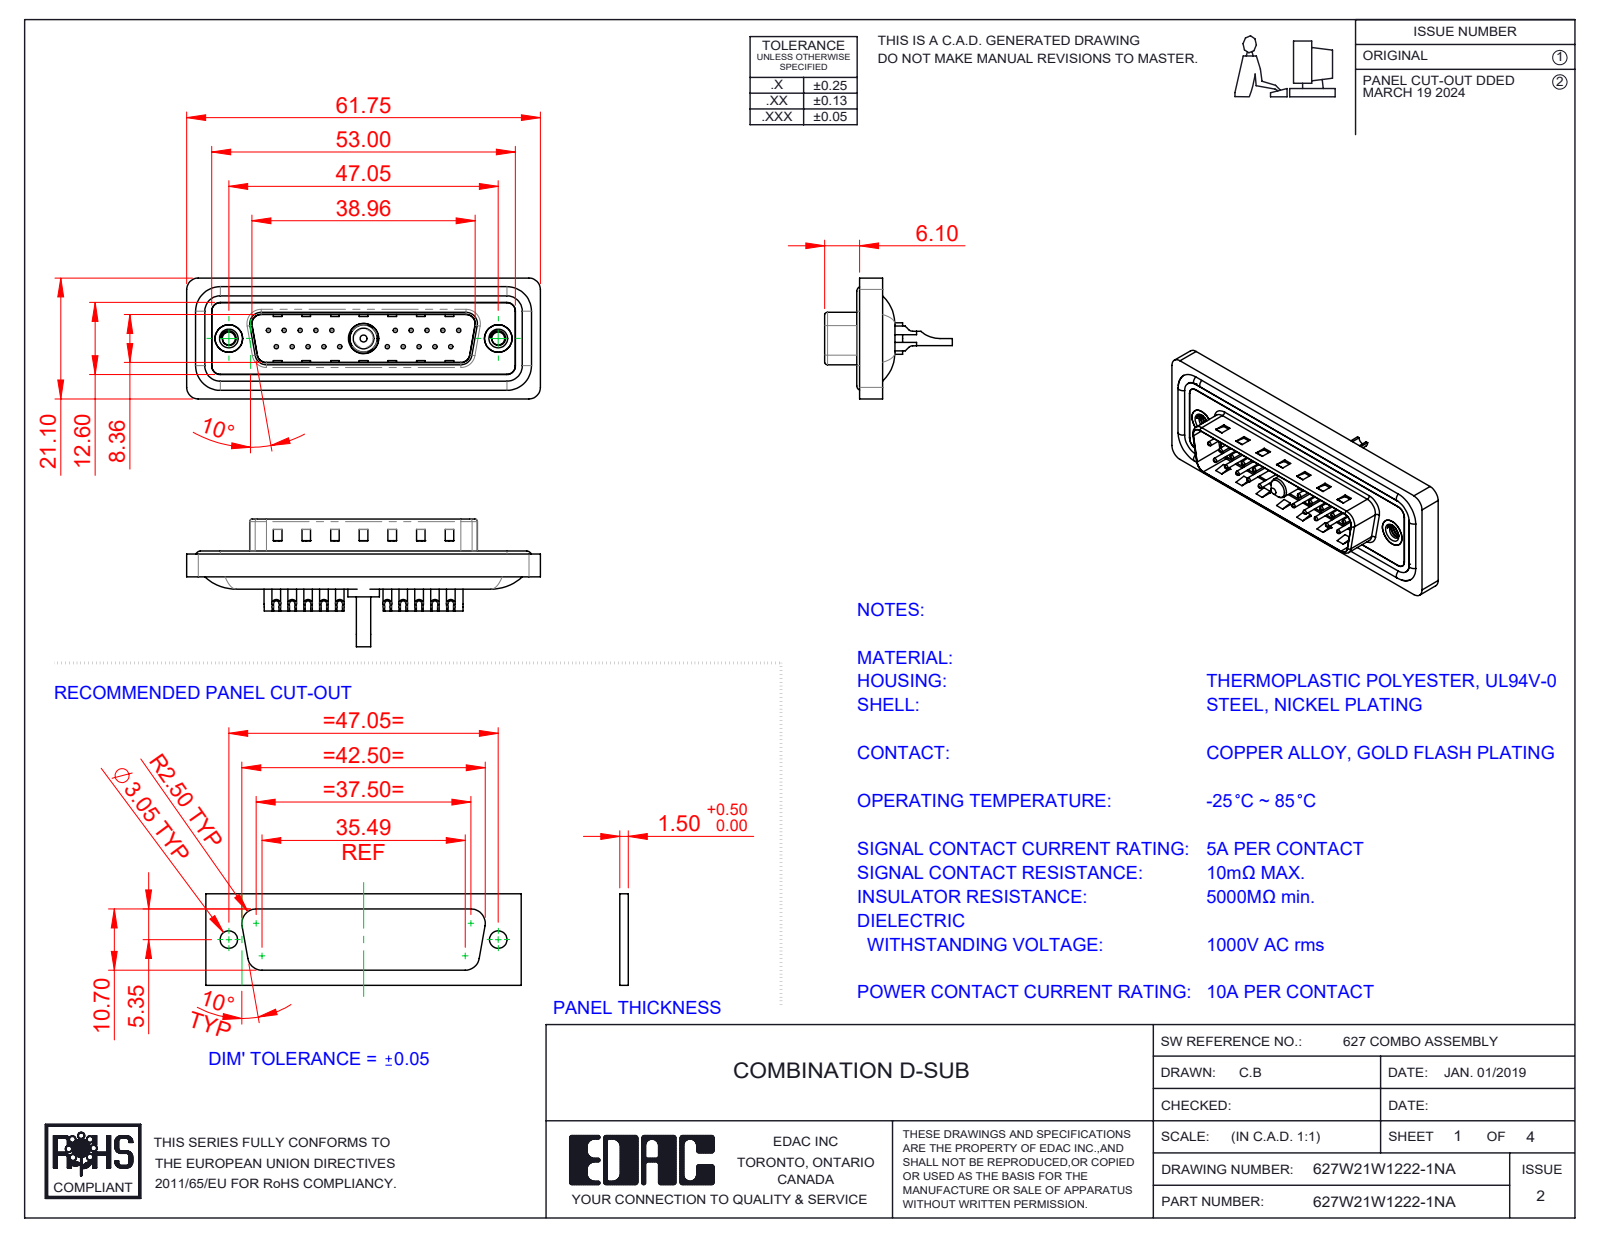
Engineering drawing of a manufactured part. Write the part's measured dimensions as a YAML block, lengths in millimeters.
part_name: "627Combo Waterproof Housing_25 Contacts; 627W21W1222-1NA; 627Combo Shell Rear_25 Contacts; 627Combo Contact Row 2_22 (+5 more)"
step_written_by: "SolidWorks 2023 (CONFIG_CONTROL_DESIGN)"
units: millimeters
bodies: {solids: 29, faces: 1266, planar: 401, cylindrical: 532, other: 333}
overall_size: [61.75, 22.3, 21.1]
volume: 7227
surface_area: 12158
round_holes:
  - {diameter: 0.75, count: 20}
  - {diameter: 1, count: 20}
  - {diameter: 1.6, count: 20}
  - {diameter: 2, count: 20}
  - {diameter: 2.26, count: 2}
  - {diameter: 4, count: 2}
  - {diameter: 4.8, count: 2}
  - {diameter: 5, count: 2}
  - {diameter: 1.7, count: 1}
  - {diameter: 4.85, count: 1}
  - {diameter: 5.3, count: 1}
round_bosses_or_shafts:
  - {diameter: 1.5, count: 20}
  - {diameter: 1.6, count: 4}
  - {diameter: 4.9, count: 2}
  - {diameter: 5.5, count: 1}
  - {diameter: 5.2, count: 1}
  - {diameter: 4.75, count: 1}
  - {diameter: 3.75, count: 1}
  - {diameter: 3.6, count: 1}
partial_cylinders:
  - {radius: 1.5, count: 22}
  - {radius: 2, count: 18}
  - {radius: 0.5, count: 8}
  - {radius: 1.6, count: 8}
  - {radius: 1, count: 6}
  - {radius: 0.25, count: 4}
  - {radius: 0.6, count: 4}
  - {radius: 0.65, count: 4}
face_to_face_distances: [0.4, 1.5, 1.1, 1.6, 0.5, 3.1, 2.9, 4.1, 0.82, 9.58]
hole_center_spacings: [3.16, 2.77, 5.54, 8.31, 5.04, 19.39, 20.97, 22.16]
